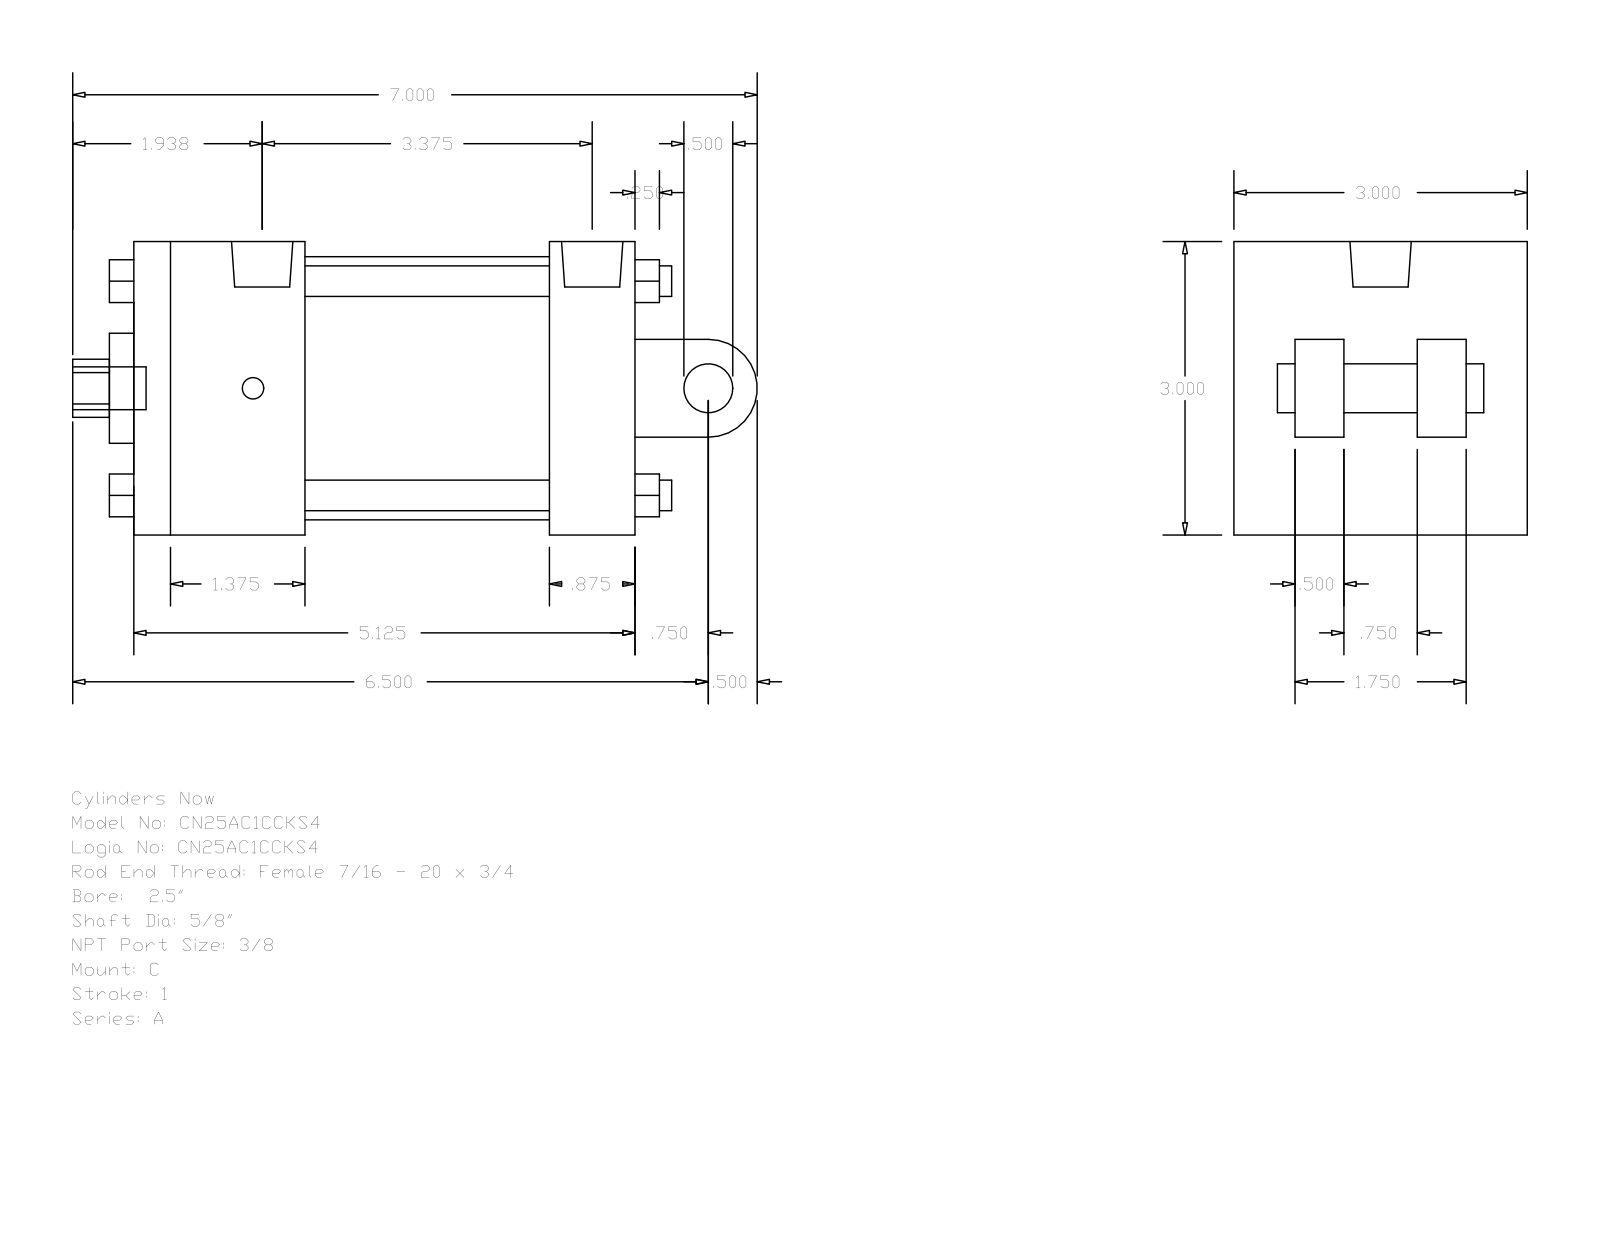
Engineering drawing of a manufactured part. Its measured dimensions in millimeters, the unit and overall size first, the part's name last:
Units: millimetres
Overall size (bounding box): 177.8 × 76.2 × 76.2
Round holes (diameter × count): ⌀5.56 ×2, ⌀15.88 ×1, ⌀15.93 ×1, ⌀28.57 ×1, ⌀68.33 ×1
Round bosses / shafts (diameter × count): ⌀7.94 ×4, ⌀5.56 ×2, ⌀15.93 ×1, ⌀12.7 ×1, ⌀11.11 ×1
Partial cylindrical surfaces — rounded edges, fillets, slot ends (radius × count): R7.54 ×1, R12.7 ×1
Main face-to-face distances: 76.2, 130.17, 63.5, 44.45, 107.95, 85.72, 22.22, 50.8, 12.7, 15.87
Hole centre spacings: 2.38
Bodies: 0 solids, 135 faces (102 planar, 33 cylindrical, 0 other)
Part name (STEP PRODUCT): A_C__0250_0.625
STEP written by: GSSL Pune (CONFIG_CONTROL_DESIGN)
